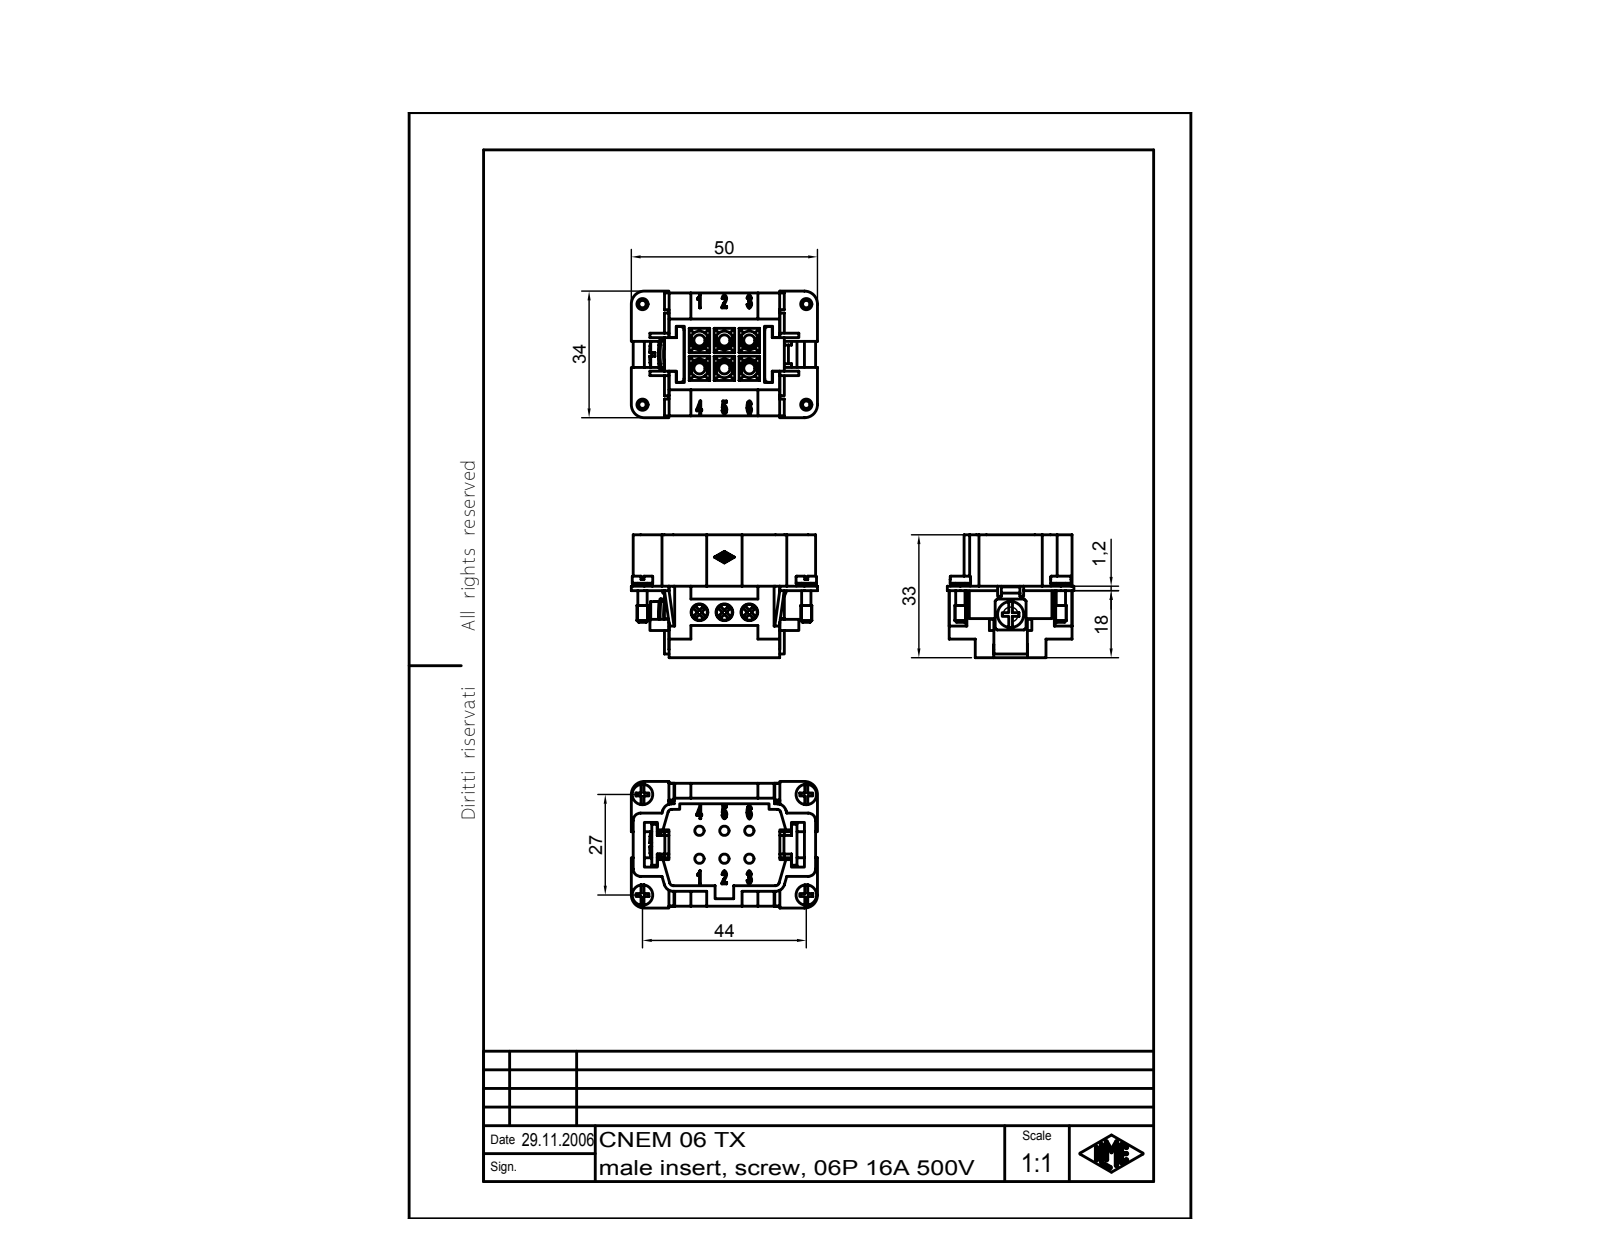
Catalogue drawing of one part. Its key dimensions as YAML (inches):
part_name: "CNEM 06 TX"
step_written_by: "Autodesk Inventor 7 (AUTOMOTIVE_DESIGN)"
units: inches
bodies: {solids: 1, faces: 897, planar: 423, cylindrical: 105, other: 369}
overall_size: [1.969, 1.339, 1.299]
volume: 1.227
surface_area: 26.39
round_holes:
  - {diameter: 0.118, count: 3}
  - {diameter: 0.177, count: 3}
  - {diameter: 0.197, count: 3}
  - {diameter: 0.1, count: 2}
  - {diameter: 0.128, count: 1}
round_bosses_or_shafts:
  - {diameter: 0.098, count: 5}
  - {diameter: 0.165, count: 3}
  - {diameter: 0.217, count: 2}
  - {diameter: 0.209, count: 2}
  - {diameter: 0.118, count: 2}
  - {diameter: 0.276, count: 1}
partial_cylinders:
  - {radius: 0.004, count: 14}
  - {radius: 0.039, count: 6}
  - {radius: 0.079, count: 6}
  - {radius: 0.098, count: 4}
  - {radius: 0.083, count: 3}
  - {radius: 0.138, count: 2}
  - {radius: 0.217, count: 1}
face_to_face_distances: [0.059, 0.118, 0.157, 0.866, 0.039, 0.807, 0.217, 0.709, 0.276, 0.047]
hole_center_spacings: [0.264, 0.528, 0.714, 0.908, 0.947, 1.063, 1.101, 1.193]
